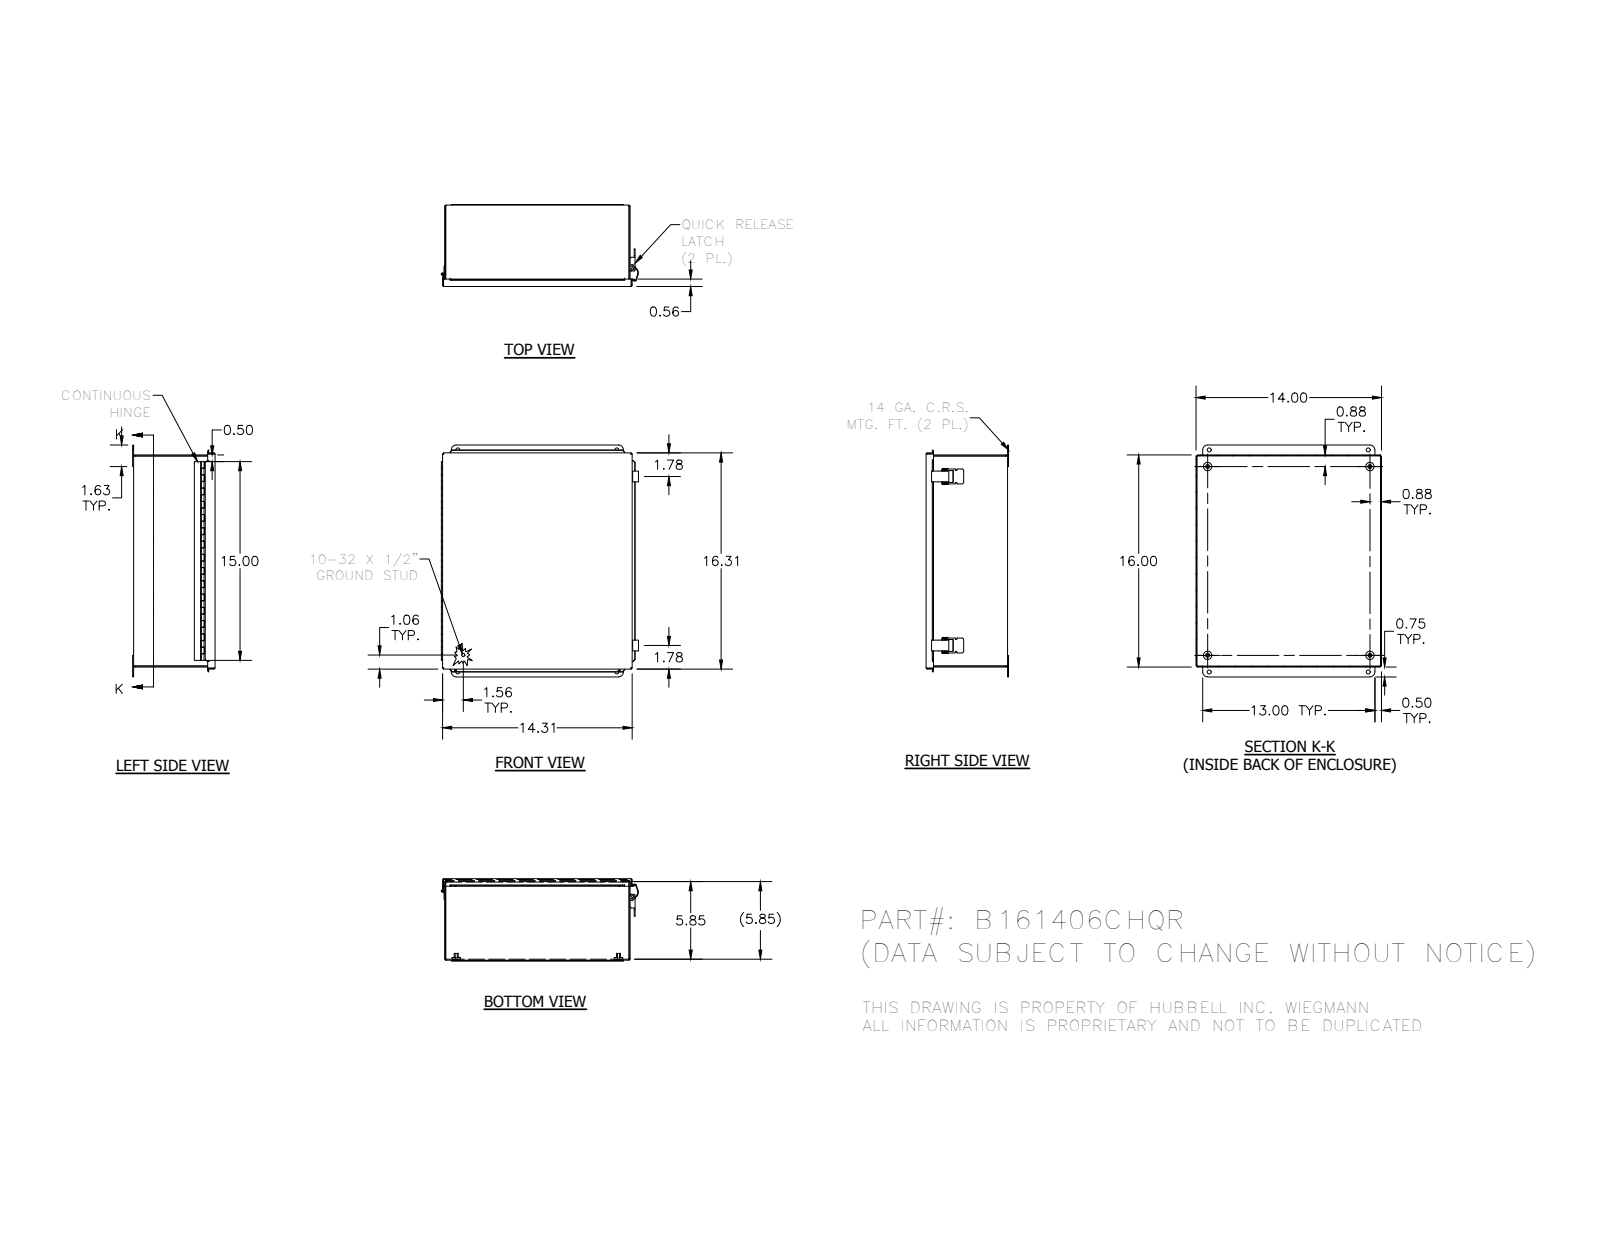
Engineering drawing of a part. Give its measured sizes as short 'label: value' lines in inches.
name: B161406CHQR; 3499; 3486; B161406CHQRBKP (+8 more)
written by: Autodesk Inventor 2012 (AUTOMOTIVE_DESIGN)
unit: in
bodies: 24 solids, 629 faces (387 planar, 195 cylindrical, 47 other)
size: 17.5 × 14.88 × 6.219
volume: 72.48 in³; area: 2 009 in²
holes: 4× ⌀0.156, 4× ⌀0.31, 2× ⌀0.14, 2× ⌀0.155, 1× ⌀0.116, 1× ⌀0.17
bosses: 4× ⌀0.625, 4× ⌀0.3, 2× ⌀0.25, 2× ⌀0.169, 2× ⌀0.136, 1× ⌀0.2, 1× ⌀0.19, 1× ⌀0.1
rounds: 20× R0.031, 8× R0.105, 7× R0.093, 5× R0.063, 4× R0.109, 4× R0.375, 2× R0.125, 1× R0.062
face distances: 0.074, 6.083, 0.062, 6.144, 6.009, 6.07, 13.926, 15.926, 14, 13.852
hole spacings: 1.256, 12.189, 15.501, 19.68, 12, 12.25, 14.25, 16.75
